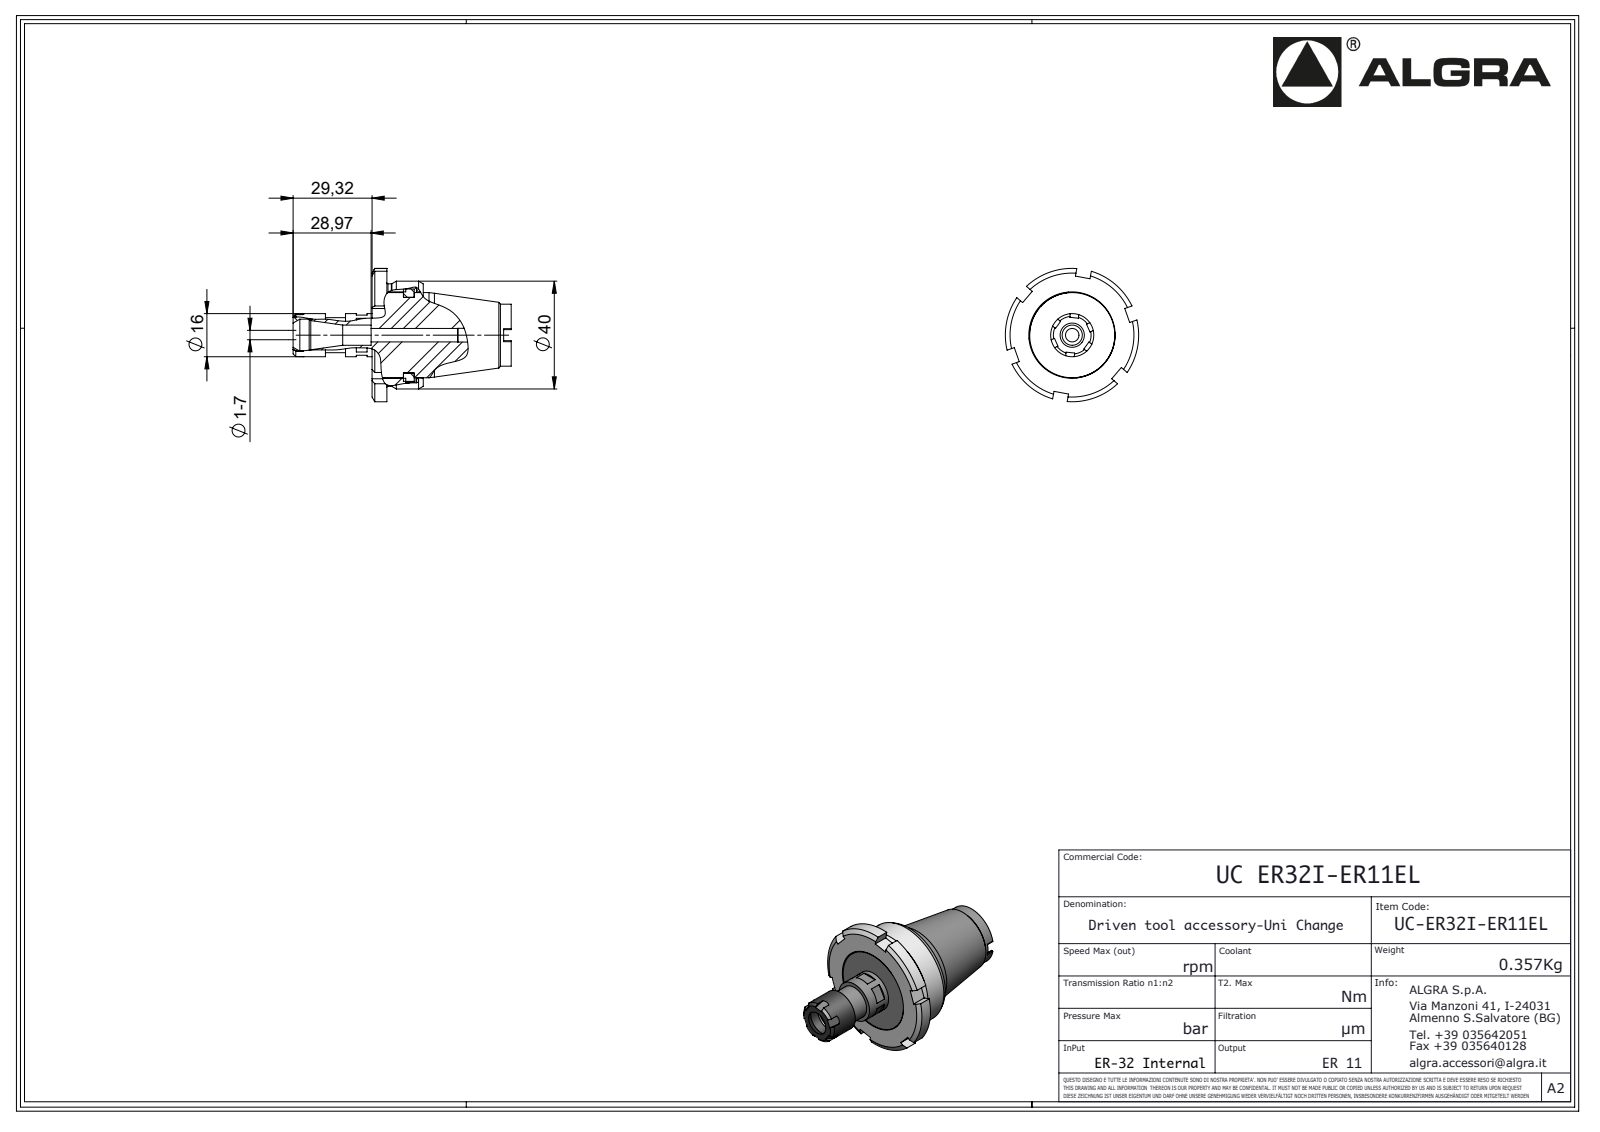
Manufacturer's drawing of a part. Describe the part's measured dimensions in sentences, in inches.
The part is named "AP-32-43-I-UC-L_Finito; AP-25-07-I-UC_Finito; 060G29_Ghiera std-ER11 (ghiera mini_eccentrica)_Finito; AP-32-05-I-UC_Finito (+2 more)". Its 3-D file was written by "SolidWorks 2016 (AUTOMOTIVE_DESIGN)". It is 7 solids with 234 faces: 103 planar, 82 cylindrical and 49 other. Overall it measures 3.188 by 1.949 by 1.949 inches. Its volume is 2.848 cubic inches and its surface area 28.41 square inches. Round holes: 2 of diameter 0.063, 2 of diameter 0.098, 1 of diameter 0.197, 1 of diameter 0.201, 1 of diameter 0.295, 1 of diameter 0.468, 1 of diameter 1.107, 1 of diameter 1.262, 1 of diameter 1.398. Round bosses or shafts: 2 of diameter 0.079, 2 of diameter 0.059, 1 of diameter 1.575, 1 of diameter 1.496, 1 of diameter 1.244, 1 of diameter 1.102, 1 of diameter 0.906, 1 of diameter 0.63. Partial cylindrical surfaces (rounded edges, fillets, slot ends): 8 of radius 0.008, 8 of radius 0.012, 4 of radius 0.004, 4 of radius 0.039, 4 of radius 0.079, 4 of radius 0.157, 2 of radius 0.049, 2 of radius 0.224. The main face-to-face distances are 0.217, 0.211, 0.157, 0.242, 0.453, 0.459, 0.4, 0.61, 0.616, 0.531. The hole center spacings are 0.285, 0.282, 0.289, 0.544, 0.545, 0.571, 0.684, 0.685.
